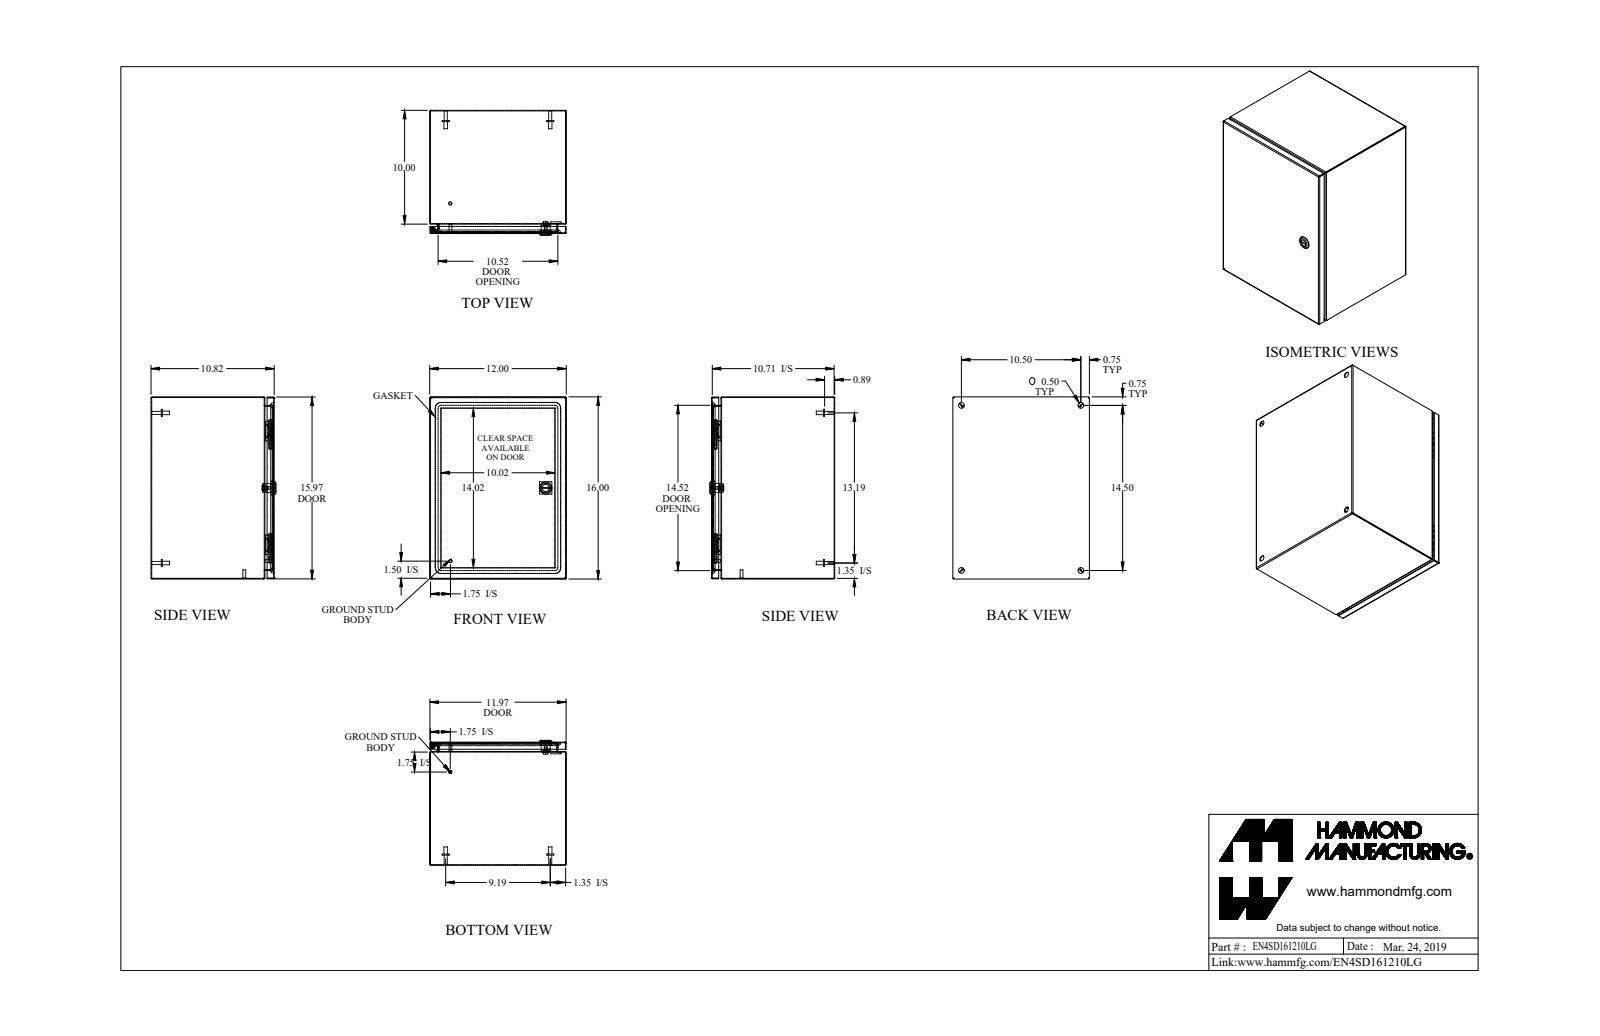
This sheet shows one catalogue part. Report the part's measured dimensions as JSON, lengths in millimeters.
{"part_name": "EN4SD161210LG_Default", "step_written_by": "SolidWorks 2019 (CONFIG_CONTROL_DESIGN)", "units": "millimeters", "bodies": {"solids": 21, "faces": 634, "planar": 285, "cylindrical": 213, "other": 136}, "overall_size": [406.4, 304.8, 278.9], "volume_mm3": 1076000, "surface_area_mm2": 1439000, "round_holes": [[12.7, 4], [4.4, 1], [5.9, 1], [6.1, 1], [6.1, 1], [15.9, 1], [19.9, 1]], "round_bosses_or_shafts": [[15.9, 4], [8, 4], [6.9, 4], [7.1, 2], [6.4, 2], [27.9, 1], [13.3, 1], [11.6, 1]], "partial_cylinders_radius": [[0.7, 21], [2.2, 21], [6.4, 16], [482.6, 8], [0.2, 4], [1.6, 4], [12.7, 4], [3.2, 2]], "face_to_face_distances": [1.4, 273.4, 303.4, 405, 272, 274.9, 301.9, 304.8, 403.5, 406.4], "hole_center_spacings": [266.7, 368.3, 454.7, 186.1, 186.1, 302.3, 302.4]}
